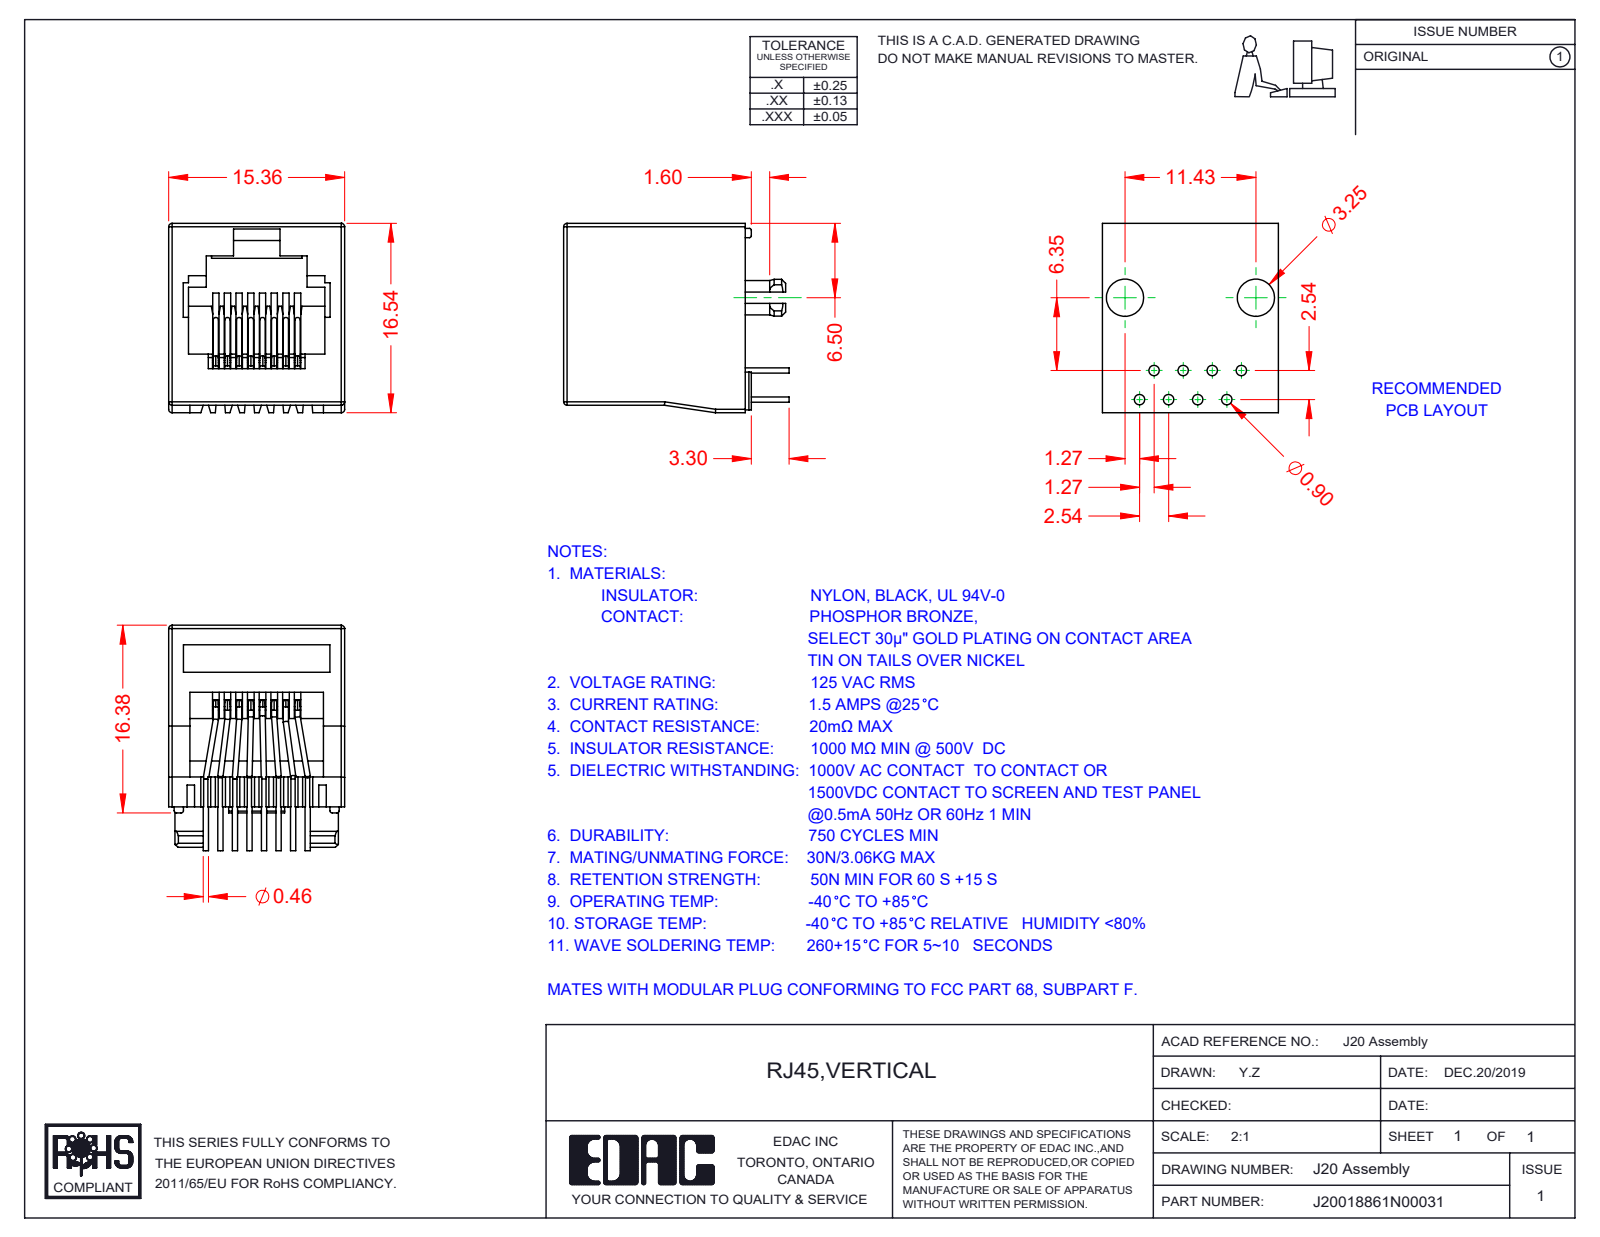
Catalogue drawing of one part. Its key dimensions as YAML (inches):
part_name: "20 Insulator; 20 Contacts; RJ20018861N00031"
step_written_by: "SolidWorks 2016 (CONFIG_CONTROL_DESIGN)"
units: inches
bodies: {solids: 9, faces: 573, planar: 332, cylindrical: 193, other: 48}
overall_size: [0.775, 0.651, 0.605]
volume: 0.118
surface_area: 4.821
round_holes:
  - {diameter: 0.079, count: 2}
round_bosses_or_shafts:
  - {diameter: 0.018, count: 45}
partial_cylinders:
  - {radius: 0.005, count: 16}
  - {radius: 0.012, count: 13}
  - {radius: 0.01, count: 9}
  - {radius: 0.008, count: 5}
  - {radius: 0.006, count: 2}
  - {radius: 0.059, count: 2}
  - {radius: 0.063, count: 2}
face_to_face_distances: [0.605, 0.068, 0.079, 0.537, 0.018, 0.624, 0.05, 0.407, 0.059, 0.554]
hole_center_spacings: [0.45]
